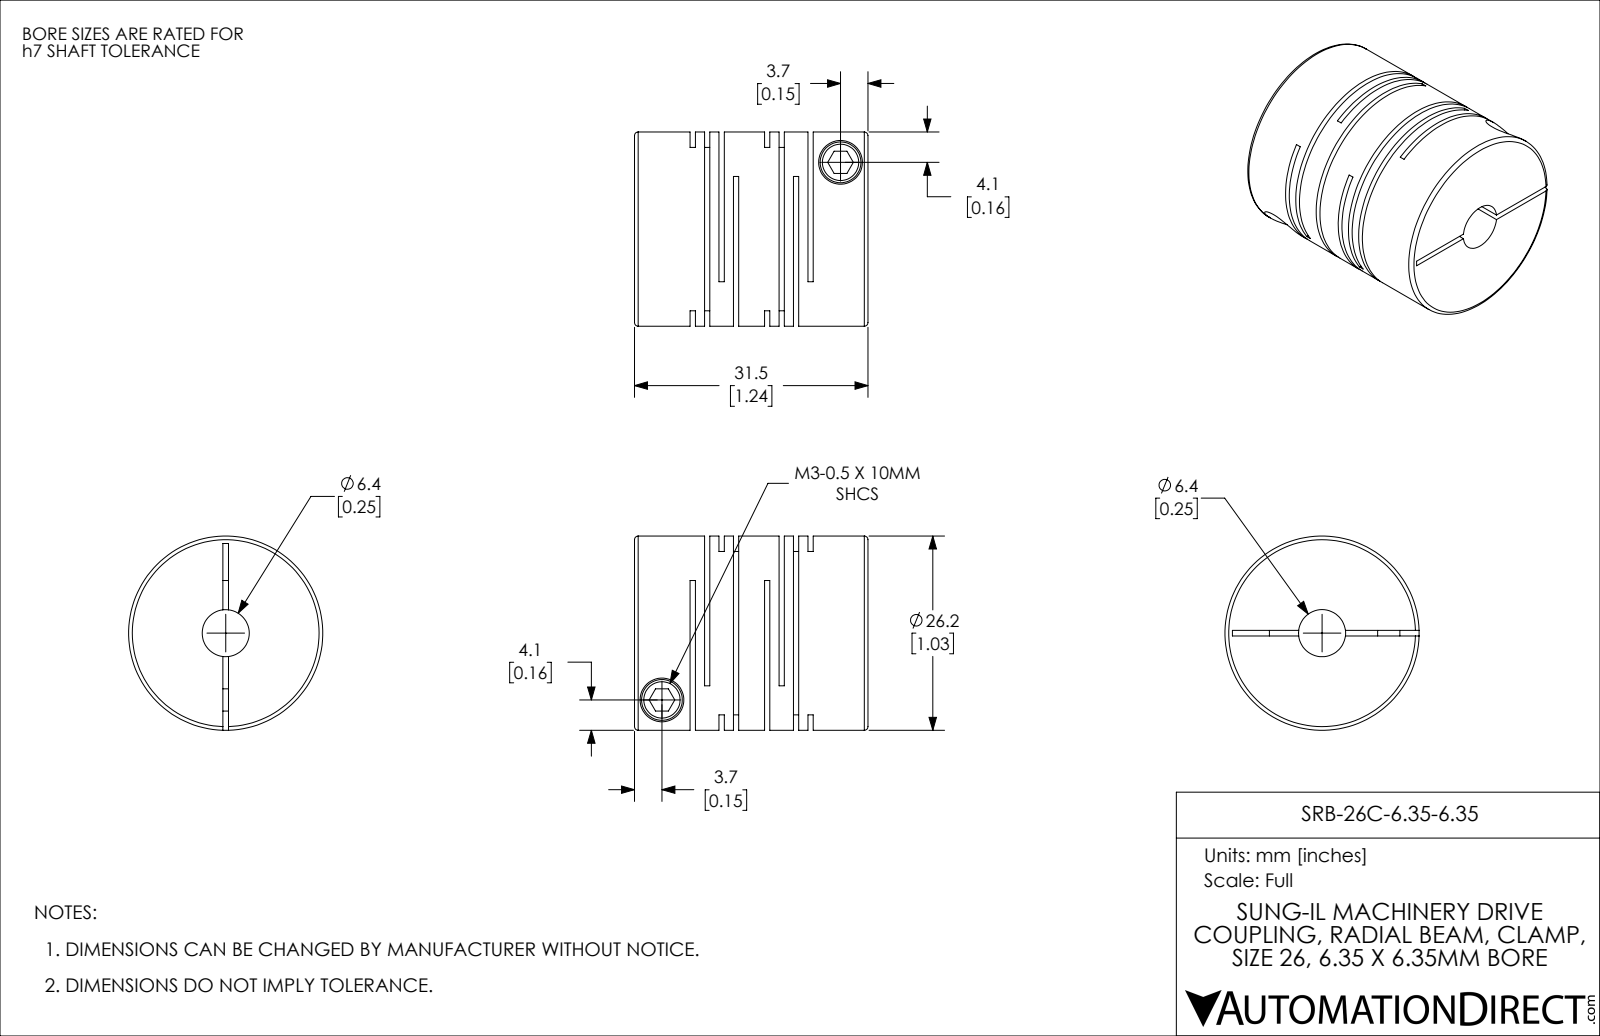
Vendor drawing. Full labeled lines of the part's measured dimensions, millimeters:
Part name (STEP PRODUCT): SRB-26C-6.35-6.35
STEP written by: SolidWorks 2021 (CONFIG_CONTROL_DESIGN)
Units: millimetres
Bodies: 1 solid, 114 faces (60 planar, 42 cylindrical, 12 other)
Overall size (bounding box): 31.5 × 26.2 × 26.2
Volume: 13 112 mm³ · Surface area: 11 371 mm²
Round holes (diameter × count): ⌀3 ×2, ⌀5.9 ×2, ⌀6.35 ×1
Round bosses / shafts (diameter × count): ⌀5.5 ×2, ⌀26.2 ×1
Main face-to-face distances: 1.95, 10.05, 0.71, 3.9, 8.1, 12, 1.24, 2.66, 9.34, 13.95
